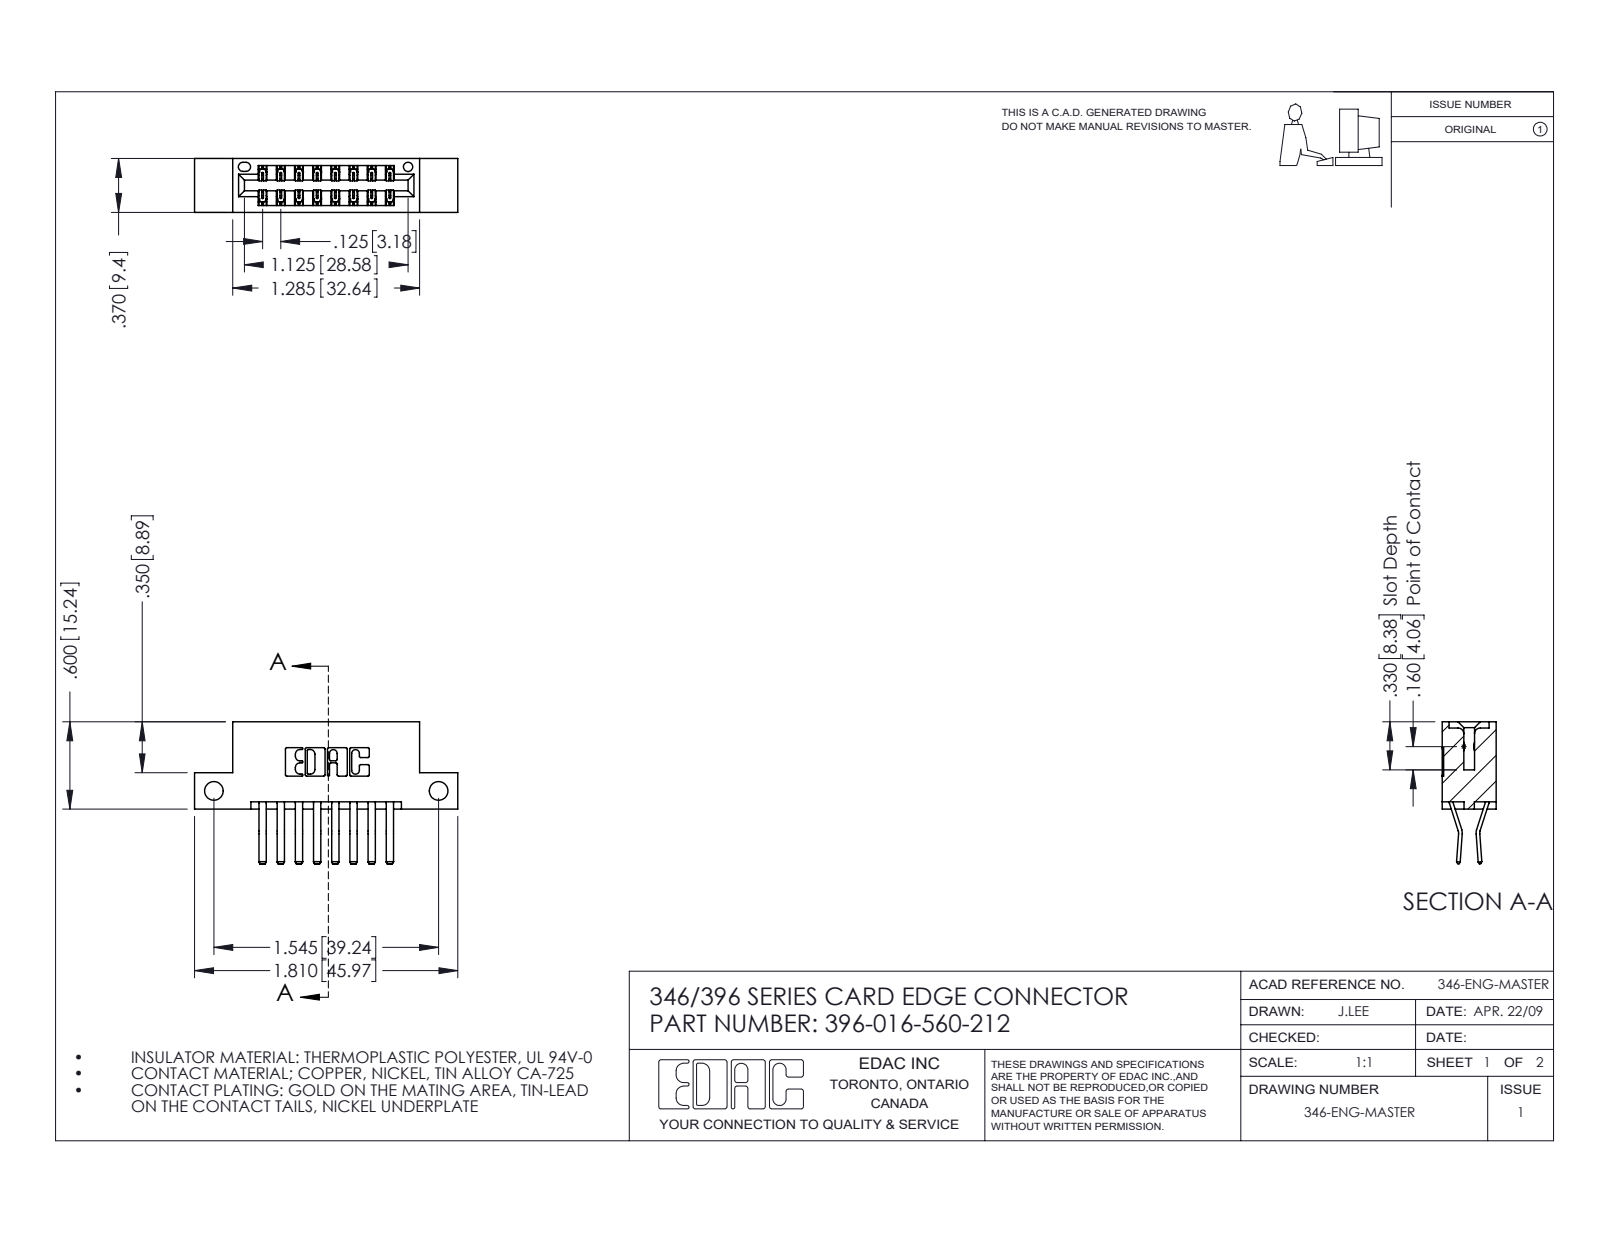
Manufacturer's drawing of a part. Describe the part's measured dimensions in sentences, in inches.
The part is named "396-016-560-212; 346 Part_Flush Mounting Lugs - Side Mount; 345-292-001_560 Tail". Its 3-D file was written by "SolidWorks 2016 (CONFIG_CONTROL_DESIGN)". It is 17 solids with 986 faces: 636 planar, 350 cylindrical and 0 other. Overall it measures 1.81 by 0.975 by 0.37 inches. Its volume is 0.259 cubic inches and its surface area 8.419 square inches. Round holes: 2 of diameter 0.128, 1 of diameter 0.064. Partial cylindrical surfaces (rounded edges, fillets, slot ends): 24 of radius 0.006, 22 of radius 0.01, 6 of radius 0.007, 6 of radius 0.031, 3 of radius 0.026, 2 of radius 0.01, 2 of radius 0.014, 2 of radius 0.022. The main face-to-face distances are 0.25, 0.048, 0.322, 0.37, 0.025, 0.5, 0.148, 0.222, 0.1, 0.174. The hole center spacings are 1.545.
